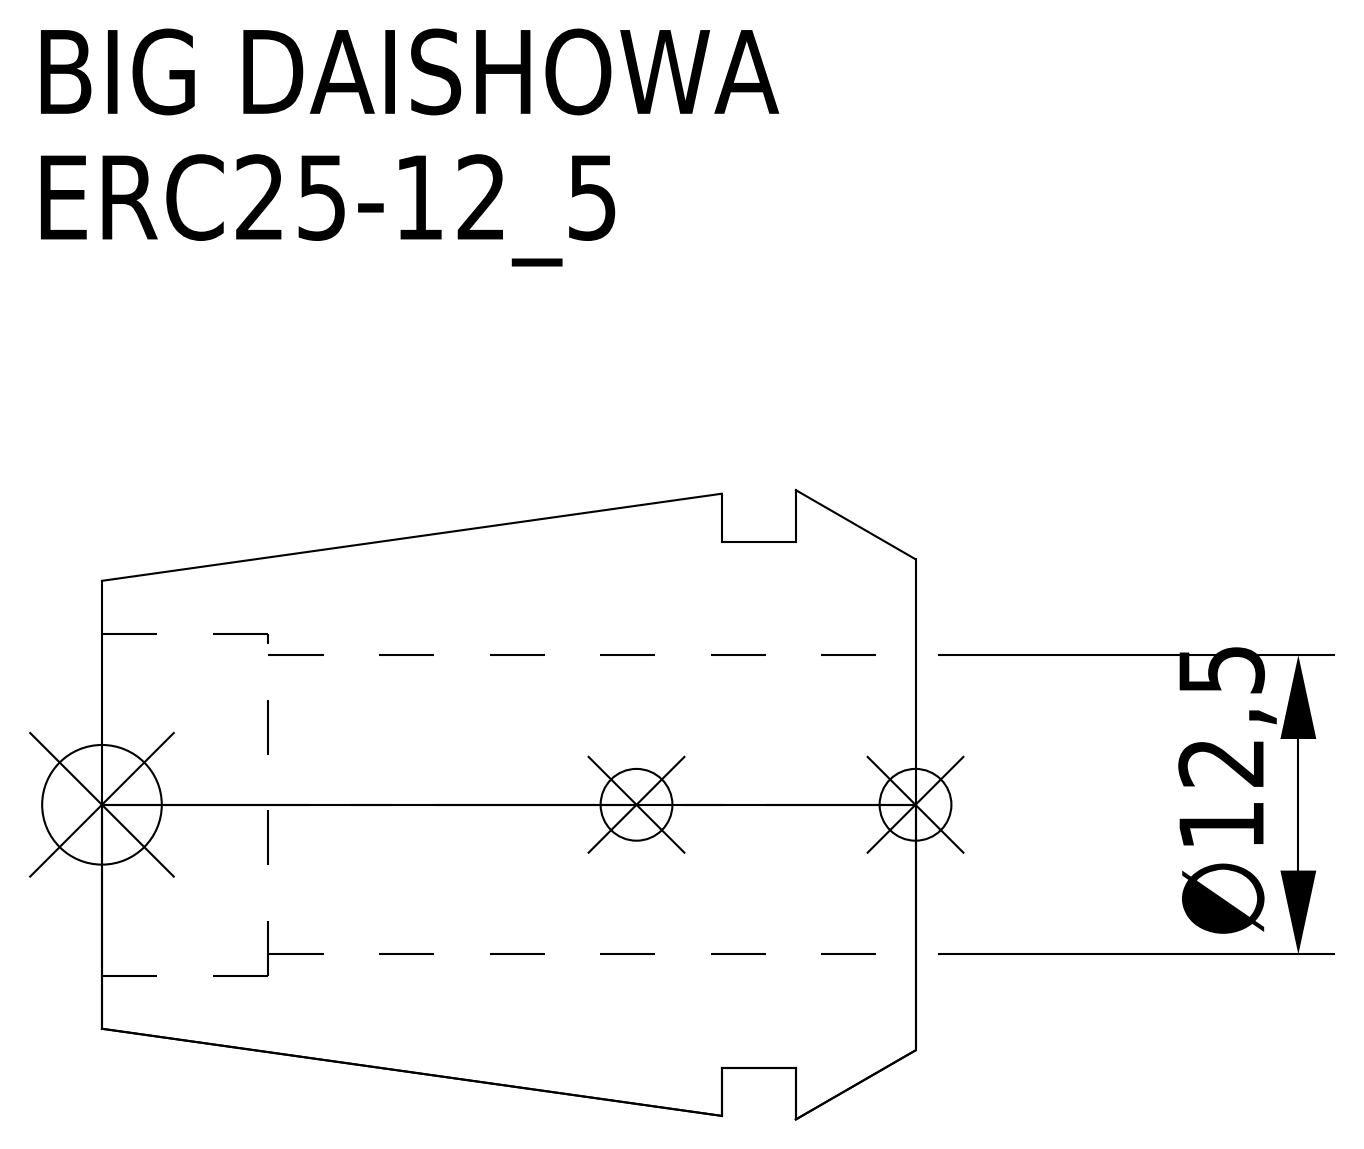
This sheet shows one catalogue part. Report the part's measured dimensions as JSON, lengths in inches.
{"part_name": "ERC25-12_5", "step_written_by": "CREO PARAMETRIC BY PTC INC, 2016380 (AUTOMOTIVE_DESIGN)", "units": "inches", "bodies": {"solids": 1, "faces": 15, "planar": 5, "cylindrical": 6, "other": 4}, "overall_size": [1.339, 1.035, 1.035], "volume_in3": 0.559, "surface_area_in2": 7.014, "round_holes": [[0.492, 1], [0.563, 1]], "round_bosses_or_shafts": [[0.866, 1]], "face_to_face_distances": [0.197, 0.319, 0.122, 1.339, 1.142, 1.02, 1.065, 0.868, 0.746, 0.274]}
